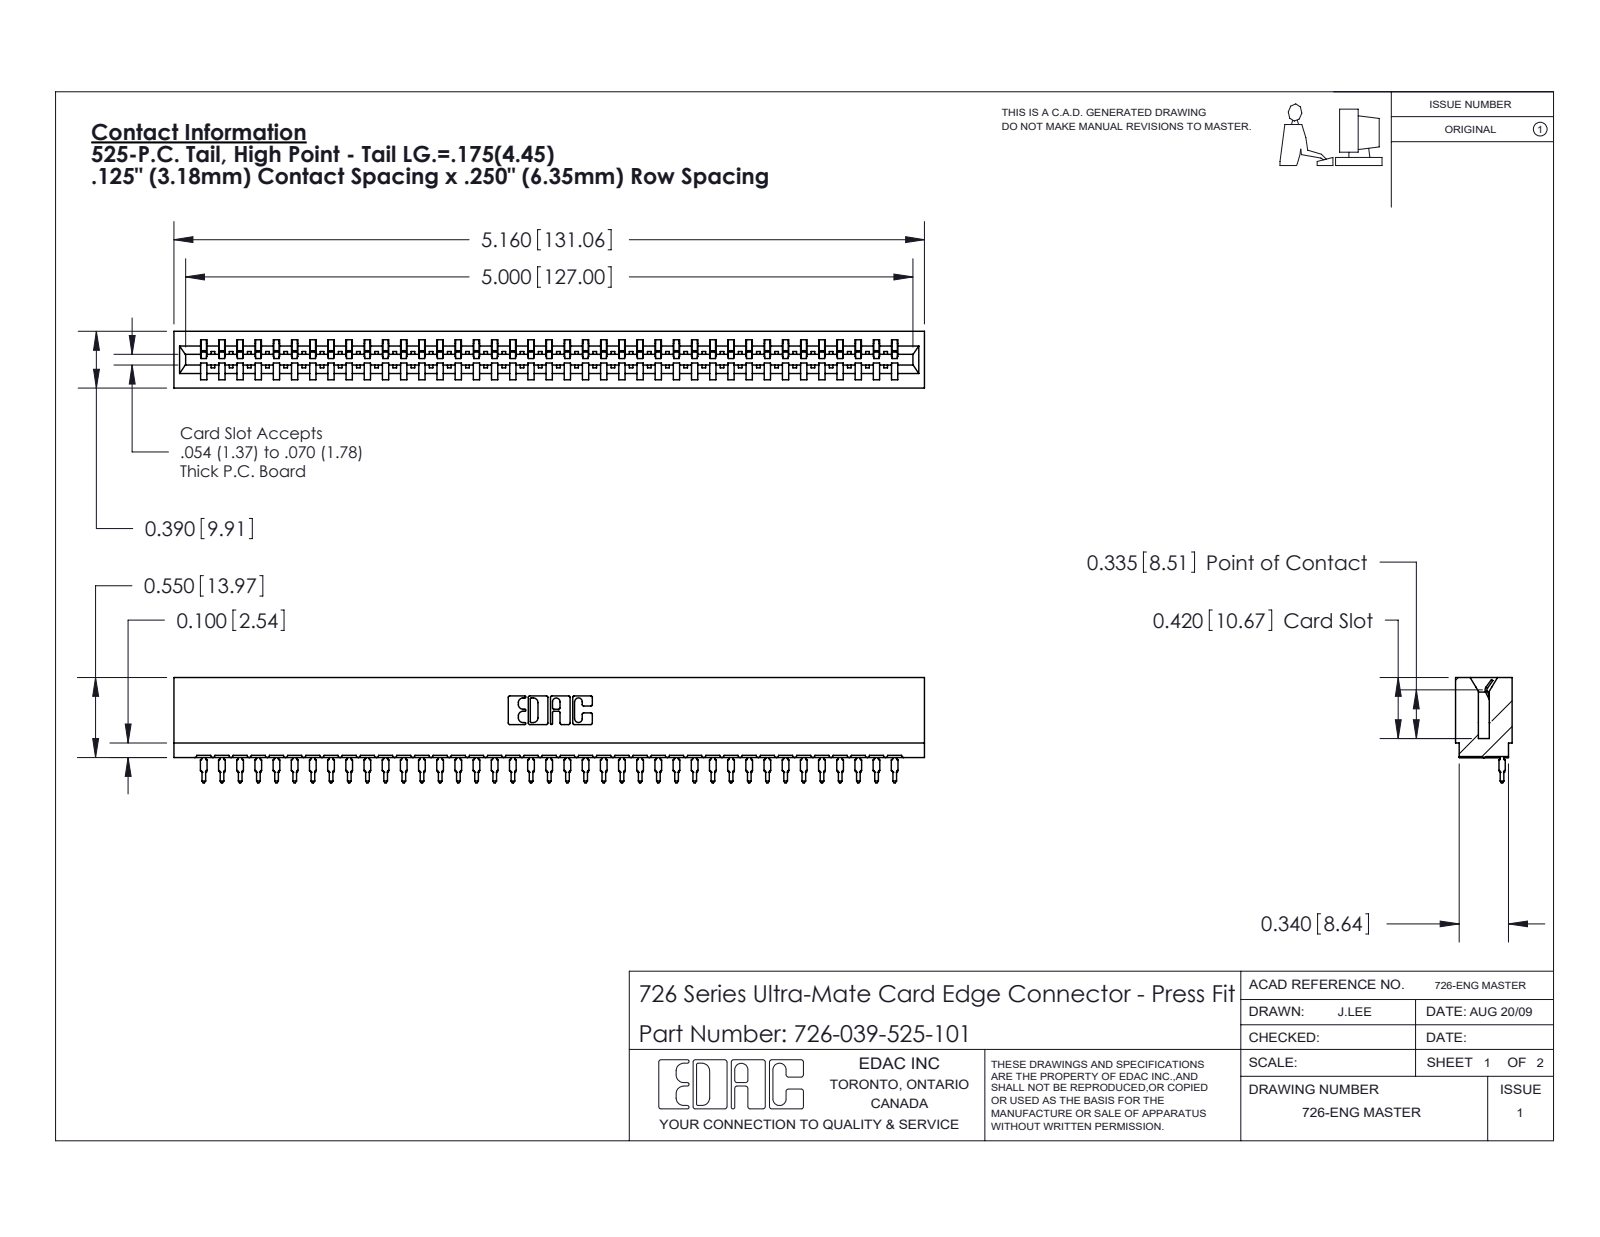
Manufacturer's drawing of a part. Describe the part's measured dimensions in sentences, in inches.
The part is named "726-039-525-101; 746-292-001_525; 726 Part_.515 Slot Depth - 01". Its 3-D file was written by "SolidWorks 2020 (CONFIG_CONTROL_DESIGN)". It is 40 solids with 4309 faces: 2512 planar, 783 cylindrical and 1014 other. Overall it measures 5.16 by 0.724 by 0.39 inches. Its volume is 0.712 cubic inches and its surface area 27.25 square inches. Partial cylindrical surfaces (rounded edges, fillets, slot ends): 78 of radius 0.021, 40 of radius 0.015, 22 of radius 0.01, 6 of radius 0.007, 6 of radius 0.031, 4 of radius 0.005, 4 of radius 0.011, 3 of radius 0.026. The main face-to-face distances are 0.057, 0.333, 0.39, 0.025, 0.307, 0.25, 0.275, 0.083, 0.365, 0.032.
